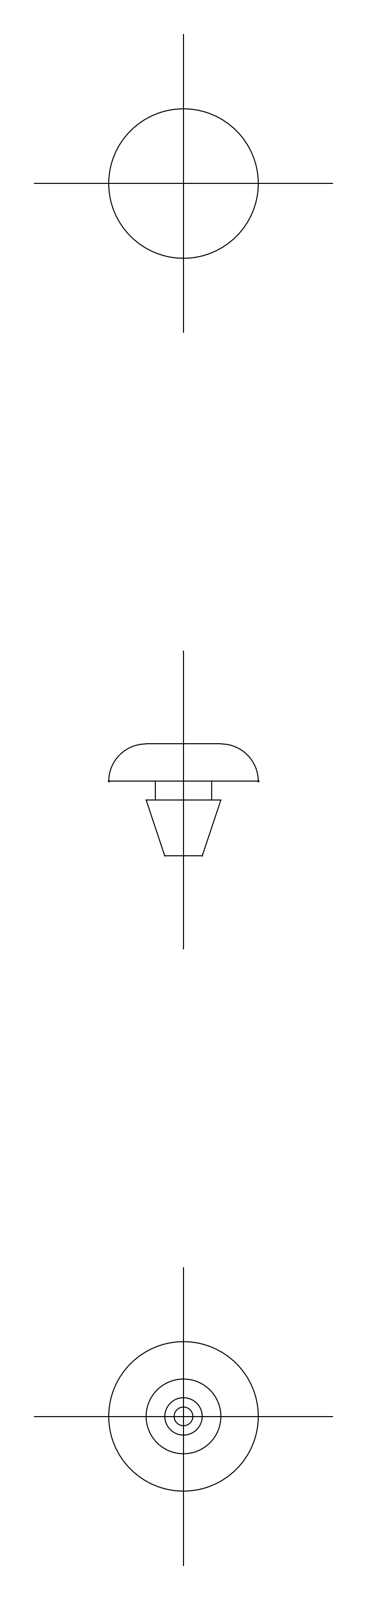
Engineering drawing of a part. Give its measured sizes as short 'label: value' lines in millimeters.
name: cushion
written by: CADfix (AUTOMOTIVE_DESIGN)
unit: mm
bodies: 1 solid, 13 faces (0 planar, 0 cylindrical, 13 other)
size: 8 × 8 × 6
volume: 107 mm³; area: 181 mm²
